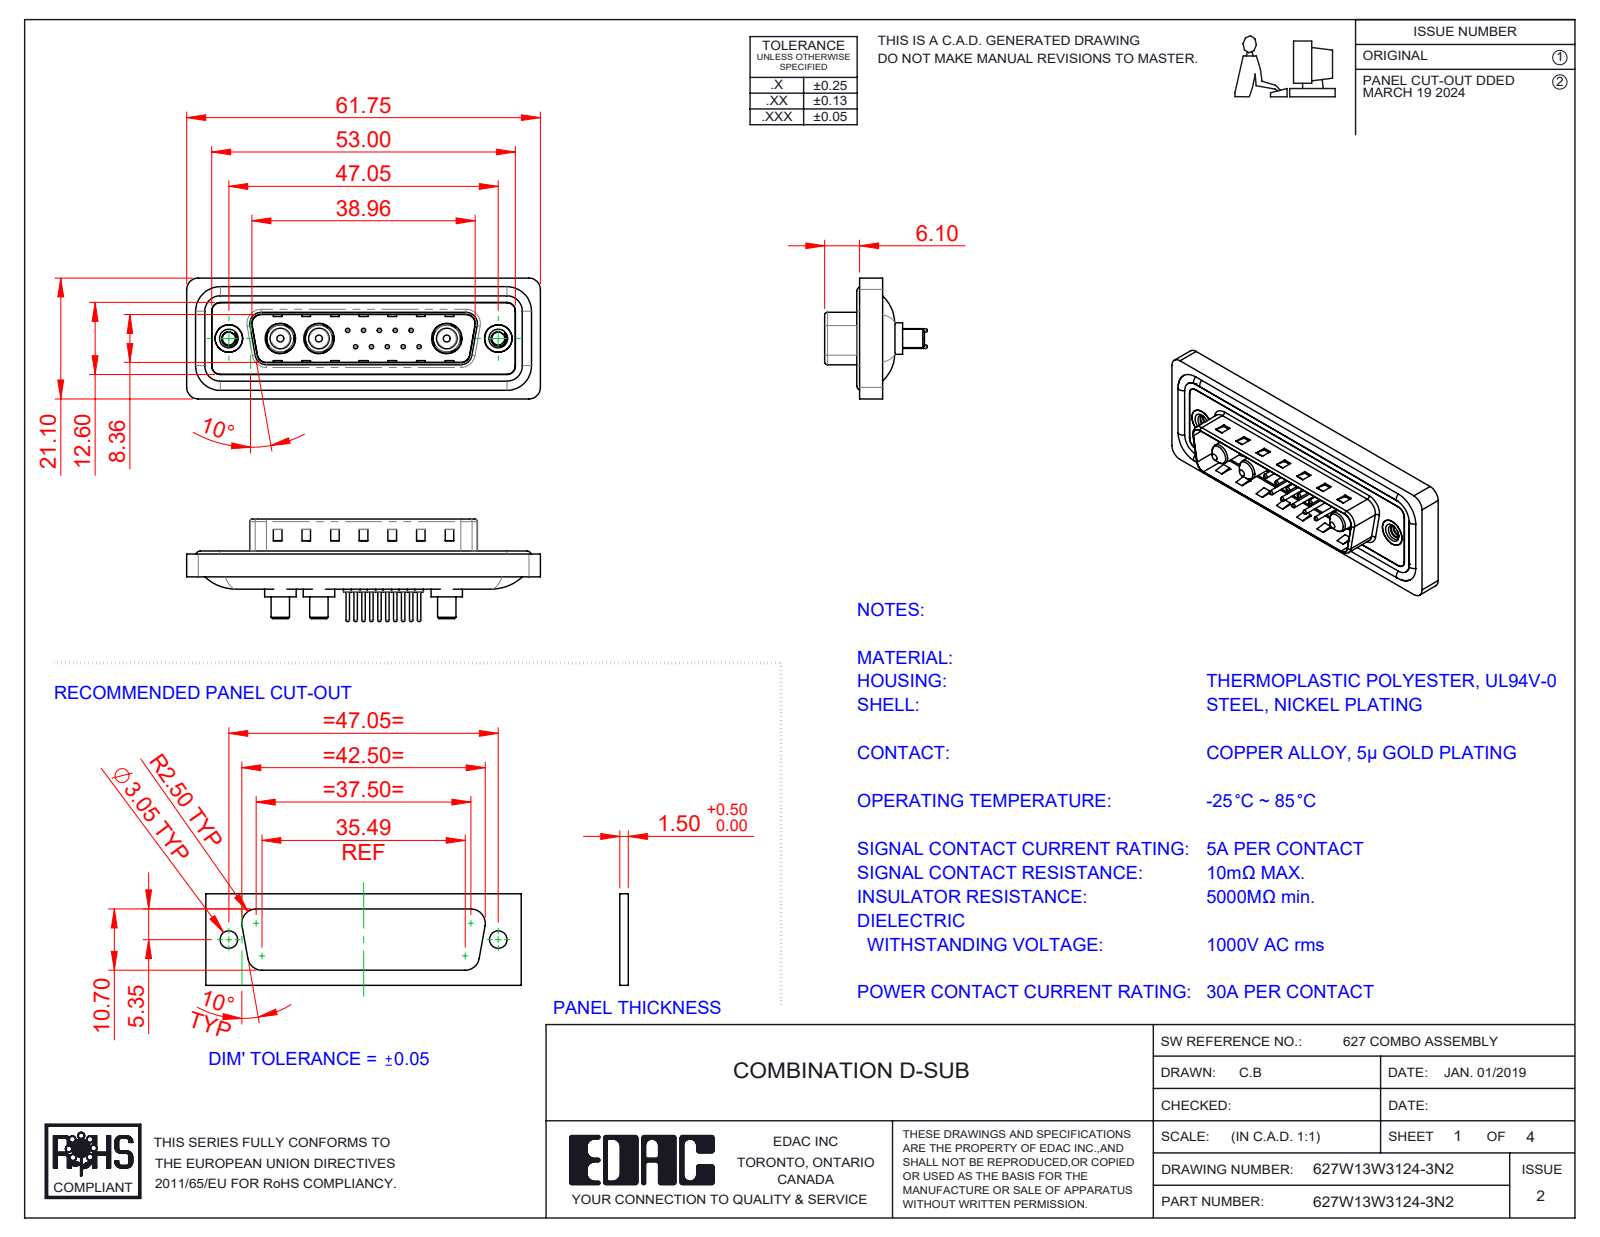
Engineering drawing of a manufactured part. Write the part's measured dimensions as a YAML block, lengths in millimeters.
part_name: "627Combo Contact Row 1_24; 627Combo Waterproof Housing_25 Contacts; Power Pin_30A S; 627Combo Threaded Rivet_2 (+5 more)"
step_written_by: "SolidWorks 2023 (CONFIG_CONTROL_DESIGN)"
units: millimeters
bodies: {solids: 23, faces: 970, planar: 309, cylindrical: 385, other: 276}
overall_size: [61.75, 21.1, 17.9]
volume: 7357
surface_area: 11888
round_holes:
  - {diameter: 0.75, count: 10}
  - {diameter: 1.6, count: 10}
  - {diameter: 2, count: 10}
  - {diameter: 4.85, count: 3}
  - {diameter: 5.3, count: 3}
  - {diameter: 2.26, count: 2}
  - {diameter: 4, count: 2}
  - {diameter: 4.8, count: 2}
  - {diameter: 5, count: 2}
round_bosses_or_shafts:
  - {diameter: 1.5, count: 10}
  - {diameter: 0.6, count: 10}
  - {diameter: 1.6, count: 4}
  - {diameter: 5.5, count: 3}
  - {diameter: 5.2, count: 3}
  - {diameter: 4.75, count: 3}
  - {diameter: 3.75, count: 3}
  - {diameter: 3.6, count: 3}
partial_cylinders:
  - {radius: 1.5, count: 22}
  - {radius: 2, count: 18}
  - {radius: 0.5, count: 8}
  - {radius: 1.6, count: 8}
  - {radius: 0.25, count: 4}
  - {radius: 0.6, count: 4}
  - {radius: 0.65, count: 4}
  - {radius: 0.9, count: 4}
face_to_face_distances: [0.4, 1.5, 1.1, 1.6, 0.5, 3.1, 2.9, 0.82, 9.58, 4.1]
hole_center_spacings: [3.16, 2.77, 5.04, 5.54, 7.49, 5.03, 8.31, 10.11]
